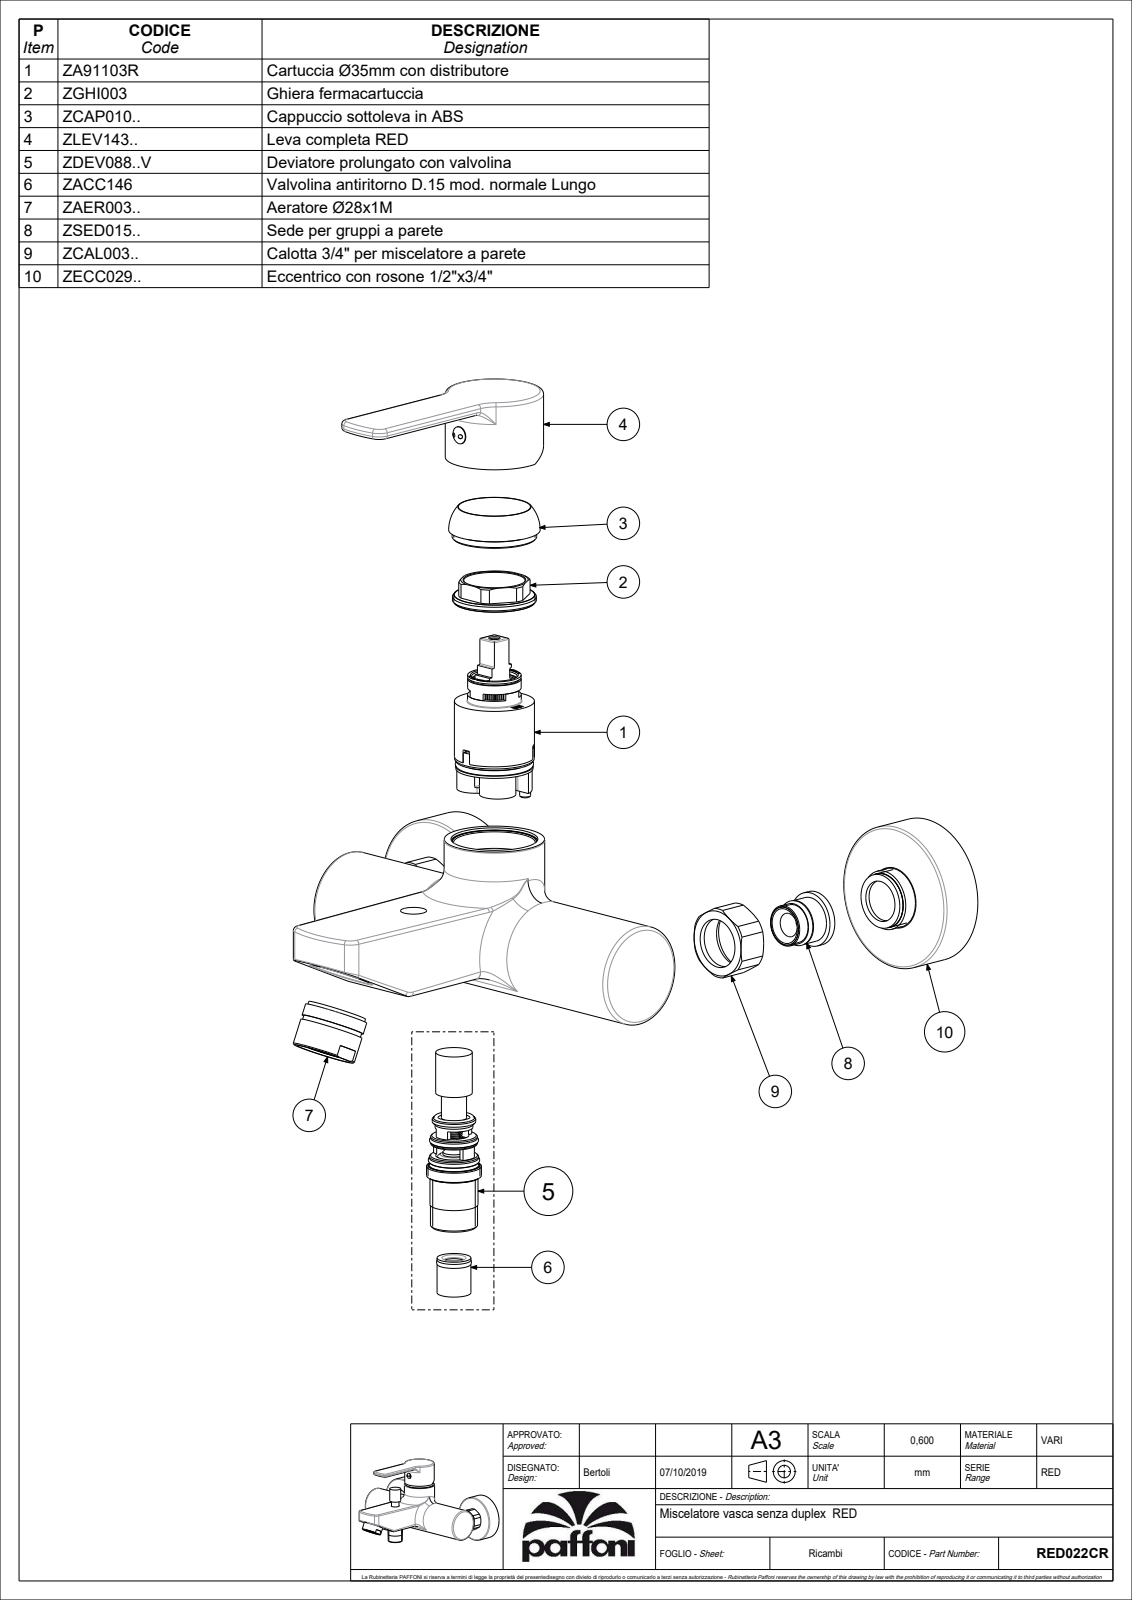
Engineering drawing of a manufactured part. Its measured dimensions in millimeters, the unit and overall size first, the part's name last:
Units: millimetres
Overall size (bounding box): 213.5 × 168.9 × 109.98
Round holes (diameter × count): ⌀12 ×4, ⌀9 ×3, ⌀19 ×3, ⌀21 ×3, ⌀25 ×3, ⌀3.3 ×2, ⌀4 ×2, ⌀5 ×2, ⌀7 ×2, ⌀8 ×2, ⌀10.5 ×2, ⌀21.5 ×2
Round bosses / shafts (diameter × count): ⌀24 ×3, ⌀63.5 ×2, ⌀44 ×2, ⌀27 ×2, ⌀19.7 ×2, ⌀16 ×2, ⌀9 ×2, ⌀43 ×1
Partial cylindrical surfaces — rounded edges, fillets, slot ends (radius × count): R0.5 ×83, R1 ×32, R0.15 ×11, R0.3 ×9, R1.5 ×6, R7 ×4, R5 ×2, R5.5 ×2
Main face-to-face distances: 3.75, 0.6, 3, 6, 27.5, 4, 51.5, 56, 4.5, 23.75
Hole centre spacings: 0.71, 8.51, 8.6, 13.04, 13.21, 13.51, 44.97, 45.54
Volume: 255 686 mm³ · Surface area: 173 319 mm²
Bodies: 7 solids, 3288 faces (2260 planar, 553 cylindrical, 475 other)
Part name (STEP PRODUCT): RED022CR
STEP written by: CREO PARAMETRIC BY PTC INC, 2020044 (CONFIG_CONTROL_DESIGN)
